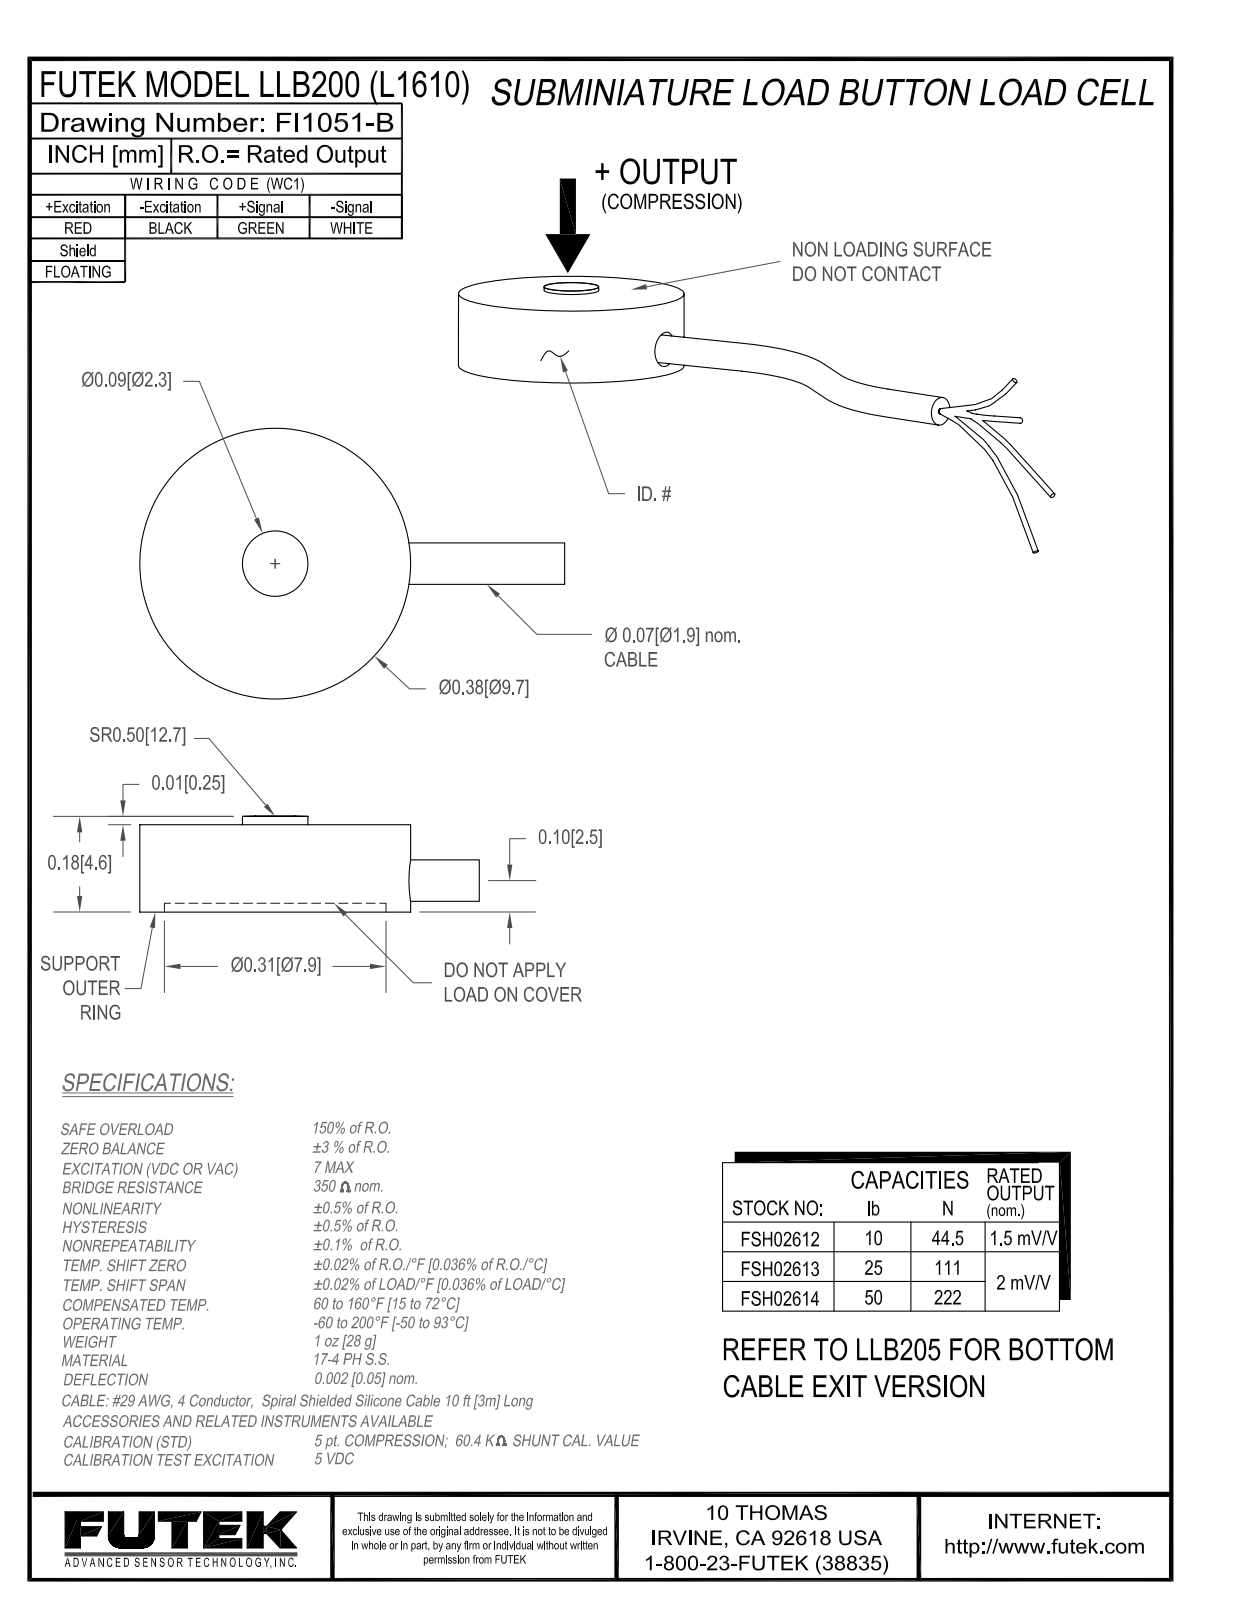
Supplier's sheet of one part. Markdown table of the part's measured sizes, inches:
| quantity | value |
| --- | --- |
| part name | LLB200; ~~PART1 (~1); F999; F999A |
| STEP written by | Autodesk Inventor 2008 (AUTOMOTIVE_DESIGN) |
| units | inches |
| bodies | 2 solids, 14 faces (7 planar, 5 cylindrical, 2 other) |
| overall size | 0.687 × 0.375 × 0.18 |
| volume | 0.017 in³ |
| surface area | 0.606 in² |
| round holes (diameter × count) | 0.085 × 1, 0.31 × 1 |
| round bosses / shafts (diameter × count) | 0.375 × 1, 0.303 × 1, 0.09 × 1 |
| main face-to-face distances | 0.142, 0.028, 0.17, 0.342, 0.5, 0.157, 0.04, 0.012, 0.13 |
